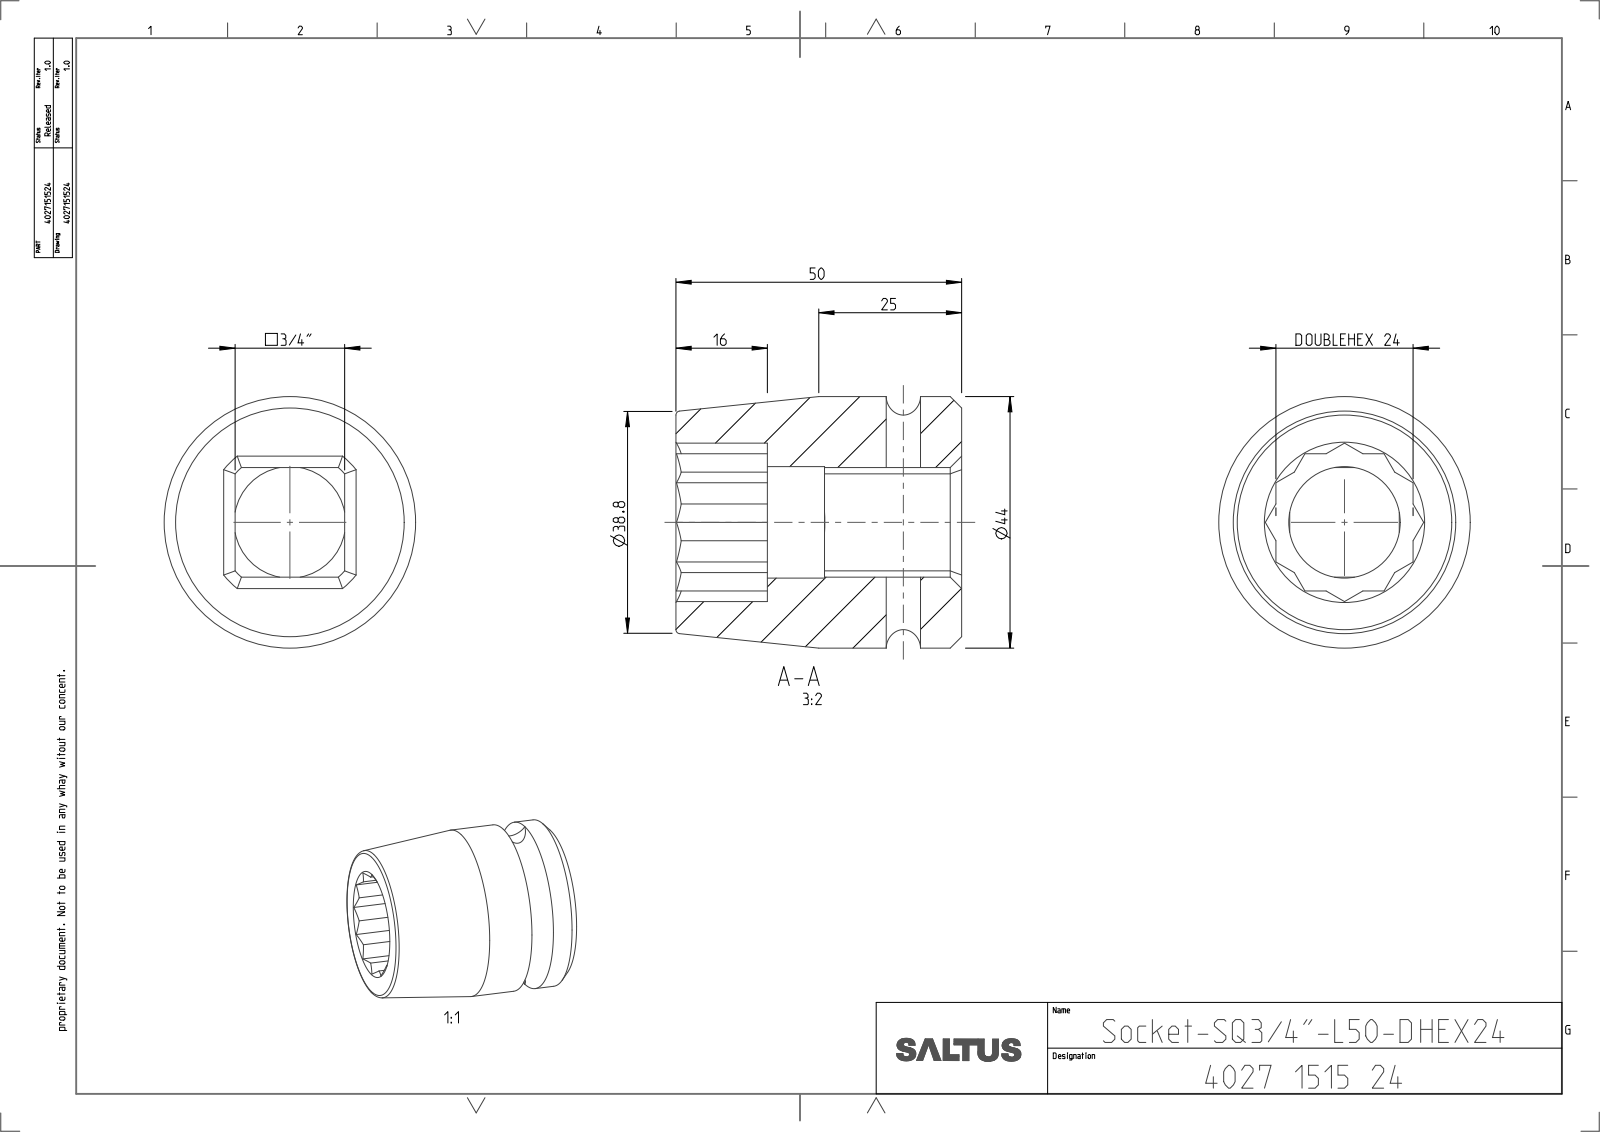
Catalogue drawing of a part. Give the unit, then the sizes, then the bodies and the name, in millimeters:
Units: millimetres
Overall size (bounding box): 50 × 44 × 44
Round holes (diameter × count): ⌀6 ×1, ⌀19.5 ×1
Round bosses / shafts (diameter × count): ⌀44 ×1
Partial cylindrical surfaces — rounded edges, fillets, slot ends (radius × count): R12.8 ×1
Main face-to-face distances: 24, 19.18, 50, 2.41, 21.59, 34, 16, 10, 26
Volume: 48 548 mm³ · Surface area: 12 959 mm²
Bodies: 1 solid, 71 faces (39 planar, 14 cylindrical, 18 other)
Part name (STEP PRODUCT): 4027151524
STEP written by: CREO PARAMETRIC BY PTC INC, 2022414 (CONFIG_CONTROL_DESIGN)
